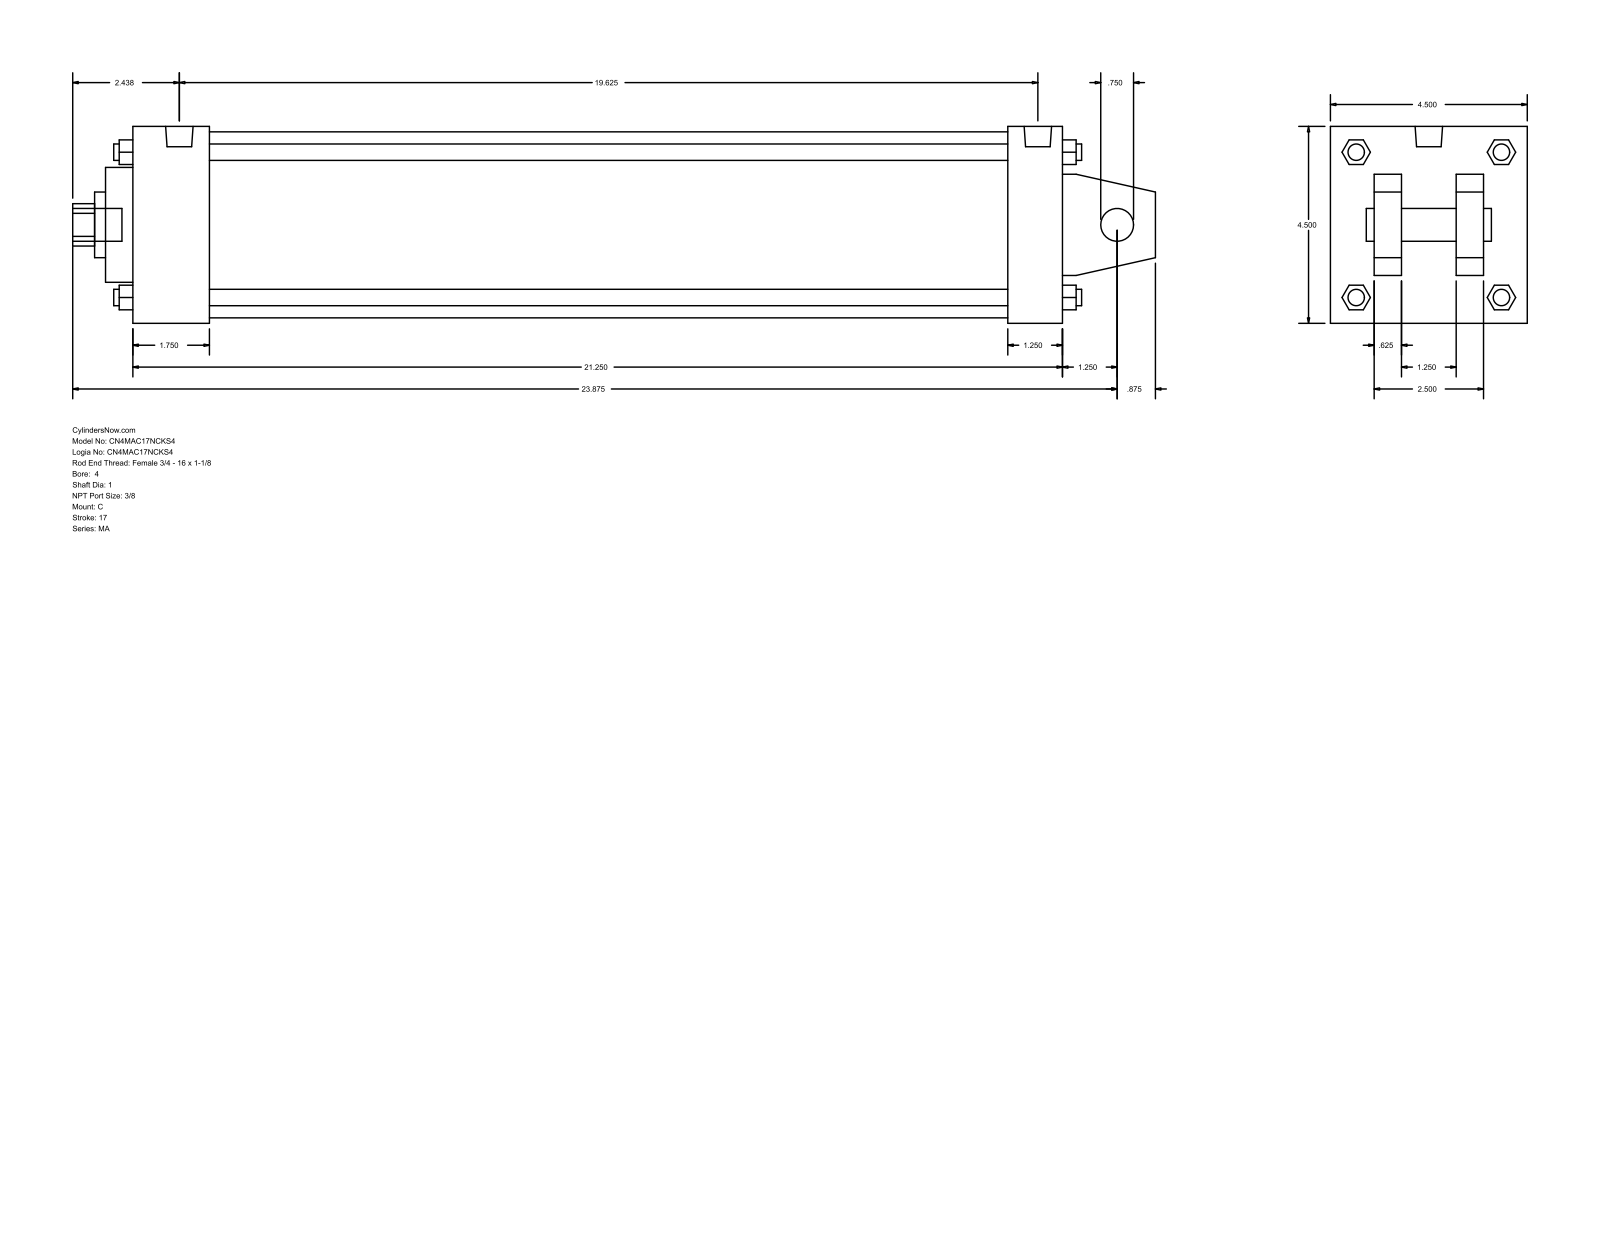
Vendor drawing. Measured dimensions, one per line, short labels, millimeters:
name: MA_C__0400_1
written by: GSSL Pune (CONFIG_CONTROL_DESIGN)
unit: mm
bodies: 0 solids, 141 faces (109 planar, 32 cylindrical, 0 other)
size: 628.65 × 114.3 × 114.3
holes: 1× ⌀19.05, 1× ⌀25.4, 1× ⌀38.1, 1× ⌀66.67, 1× ⌀107.95
bosses: 4× ⌀11.11, 4× ⌀9.53, 2× ⌀15.93, 1× ⌀19.05
rounds: 1× R12.29
face distances: 114.3, 539.75, 15.87, 73.03, 41.27, 25.4, 88.9, 47.63, 508, 31.75
